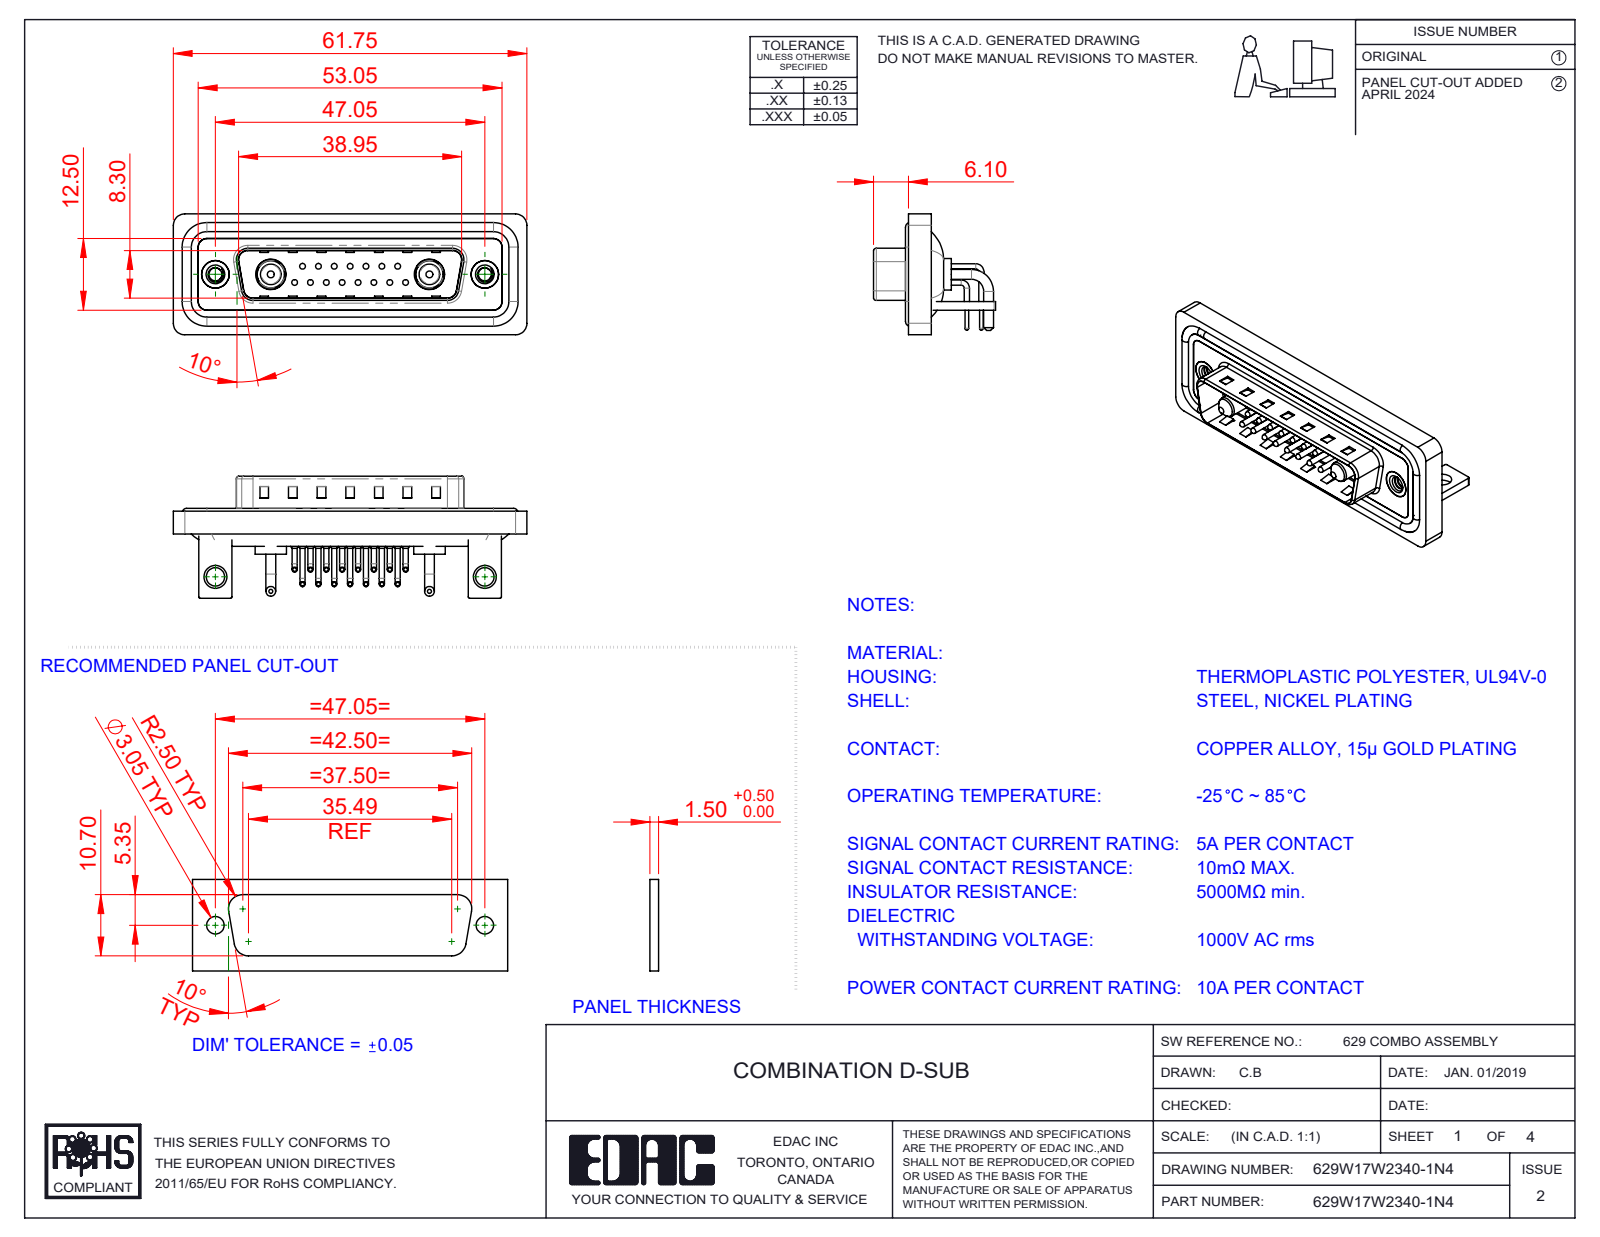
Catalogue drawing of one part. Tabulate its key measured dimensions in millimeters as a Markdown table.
| quantity | value |
| --- | --- |
| part name | 629Combo Waterproof Housing_25 Contacts; 629Combo Stabilizer Bracket; 629W17W2340-1N4; 629Combo Housing_17W2 (+6 more) |
| STEP written by | SolidWorks 2023 (CONFIG_CONTROL_DESIGN) |
| units | millimeters |
| bodies | 28 solids, 2259 faces (1209 planar, 788 cylindrical, 262 other) |
| overall size | 61.75 × 21.3 × 21.1 |
| volume | 7 674 mm³ |
| surface area | 13 086 mm² |
| round holes (diameter × count) | 0.75 × 15, 1.6 × 15, 2 × 15, 2.26 × 2, 3.2 × 2, 4 × 2, 4.8 × 2, 4.85 × 2, 5 × 2, 5.3 × 2 |
| round bosses / shafts (diameter × count) | 0.9 × 30, 1.5 × 15, 1 × 15, 0.65 × 15, 1.7 × 4, 1.6 × 4, 5.5 × 2, 5.2 × 2 |
| partial cylindrical surfaces (radius × count) | 2 × 19, 1.5 × 18, 0.25 × 16, 1.01 × 15, 0.5 × 9, 1.6 × 8, 0.6 × 4, 0.65 × 4 |
| main face-to-face distances | 0.4, 0.8, 1.5, 2.1, 2.9, 1.1, 4.1, 1.6, 4.5, 3.7 |
| hole center spacings | 3.16, 2.77, 5.54, 8.31, 5.04, 7.49, 11.08, 5.03 |
